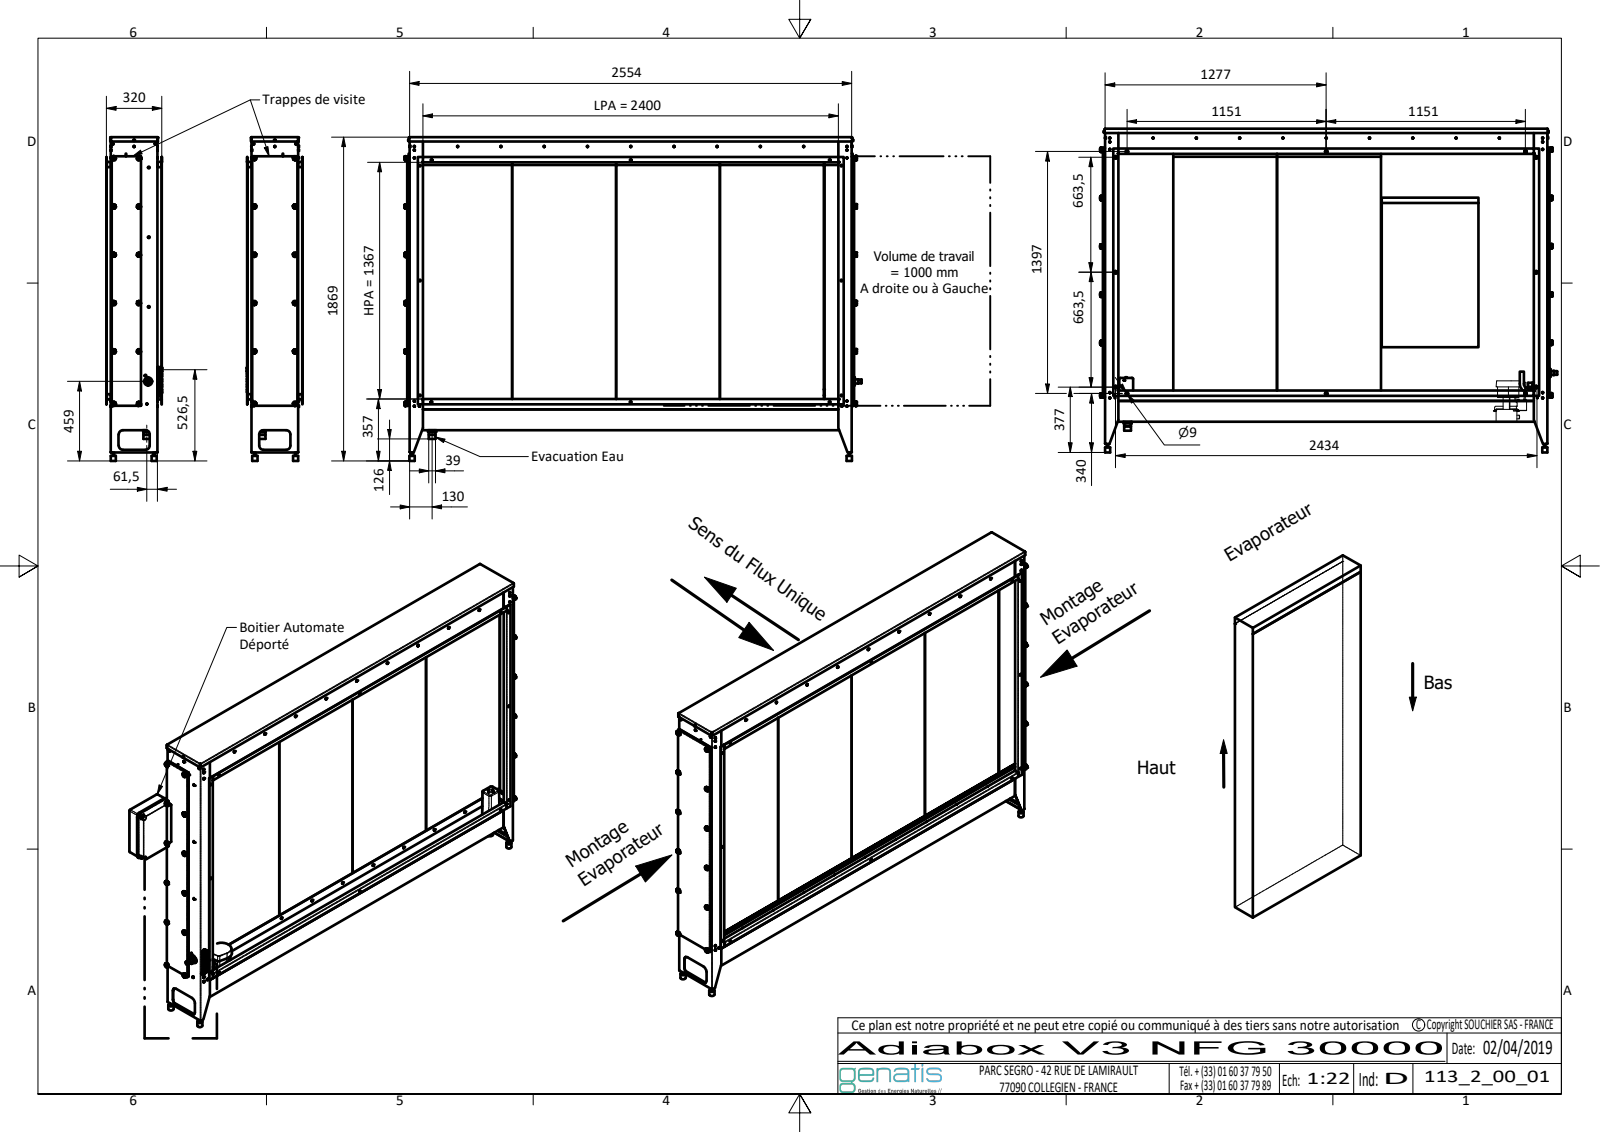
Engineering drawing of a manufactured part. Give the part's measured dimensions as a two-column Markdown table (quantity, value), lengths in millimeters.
| quantity | value |
| --- | --- |
| part name | 113_2_00_01_-_Adiabox_V3; 113_2_00_06_-_Glissiere basse assemblee; 113_3_00_11_-_Cote gauche glissiere; 113_3_00_15_-_Tole de fond pliee (+8 more) |
| STEP written by | Autodesk Inventor 2022 (AUTOMOTIVE_DESIGN) |
| units | millimeters |
| bodies | 299 solids, 7352 faces (3333 planar, 2492 cylindrical, 1527 other) |
| overall size | 2640.5 × 1869 × 323.5 |
| volume | 712 900 000 mm³ |
| surface area | 37 310 000 mm² |
| round holes (diameter × count) | 4.2 × 85, 3 × 76, 6 × 51, 4.1 × 41, 7 × 24, 9 × 15, 14 × 15, 5.2 × 14, 16 × 11, 6.5 × 7, 7.5 × 6, 11.5 × 6 |
| round bosses / shafts (diameter × count) | 7.9 × 74, 4 × 74, 11 × 47, 5 × 45, 7 × 33, 8.5 × 13, 20 × 11, 23 × 10 |
| partial cylindrical surfaces (radius × count) | 3 × 267, 8 × 168, 1.5 × 95, 12.5 × 24, 1 × 22, 5 × 18, 2 × 17, 10 × 10 |
| main face-to-face distances | 1.5, 100, 2, 265, 600, 0.5, 266.5, 62, 1690.5, 1628.5 |
| hole center spacings | 250, 500, 750, 1000, 1250, 1506.9, 251.2, 1500 |
